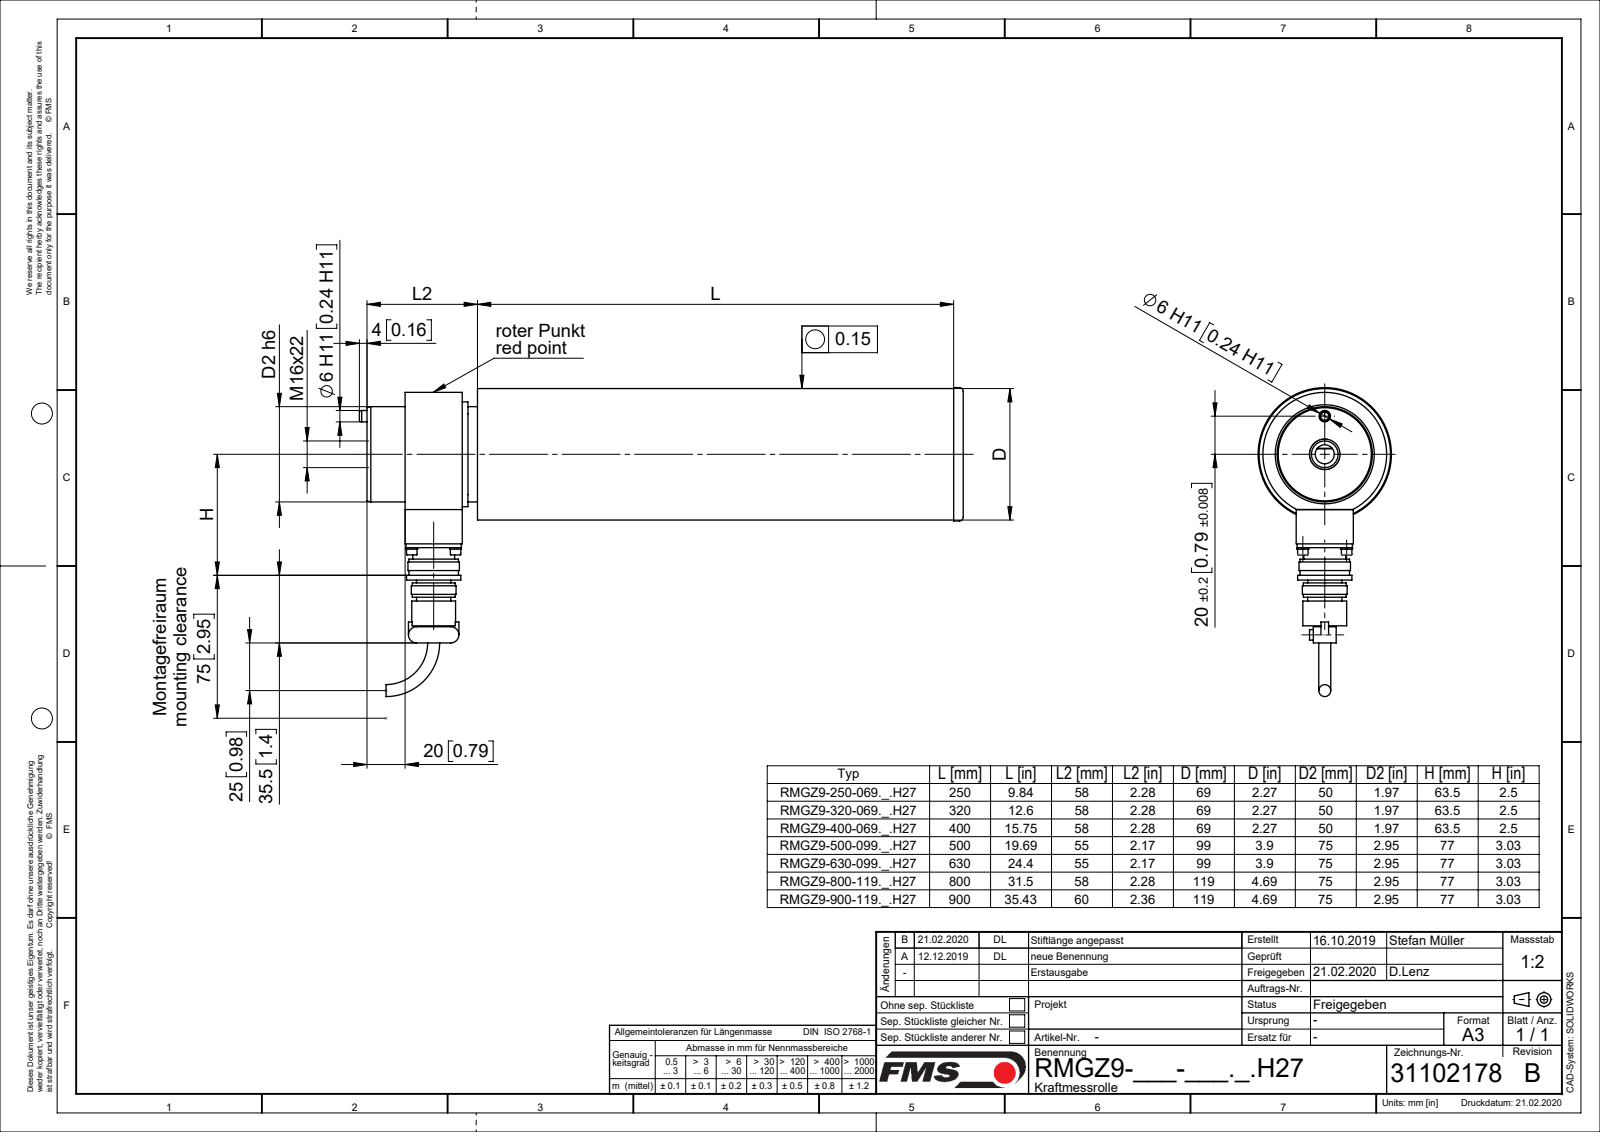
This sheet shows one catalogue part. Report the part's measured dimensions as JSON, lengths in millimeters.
{"part_name": "47679_01; Lamellenstopfen_D_070; 31102178_stp; 49026_01 (+8 more)", "step_written_by": "SolidWorks 2018 (CONFIG_CONTROL_DESIGN)", "units": "millimeters", "bodies": {"solids": 31, "faces": 597, "planar": 172, "cylindrical": 259, "other": 166}, "overall_size": [317, 162.15, 70], "volume_mm3": 629332, "surface_area_mm2": 236825, "round_holes": [[2.5, 6], [3.1, 4], [3.4, 4], [3.3, 1], [5, 1], [6, 1], [10, 1], [12, 1], [14, 1], [17, 1], [22, 1], [23, 1]], "round_bosses_or_shafts": [[5.5, 6], [6.2, 4], [3, 4], [2.5, 4], [70, 1], [69, 1], [65, 1], [58, 1]], "partial_cylinders_radius": [[0.1, 4], [11, 4], [4.19, 2], [4.25, 2], [17.5, 1], [22.2, 1], [25.37, 1]], "face_to_face_distances": [50, 3, 35, 2, 5, 258, 20, 38, 83, 18], "hole_center_spacings": [16.26, 23, 24.85, 32.53, 18.14, 20, 25.59, 37.16]}
